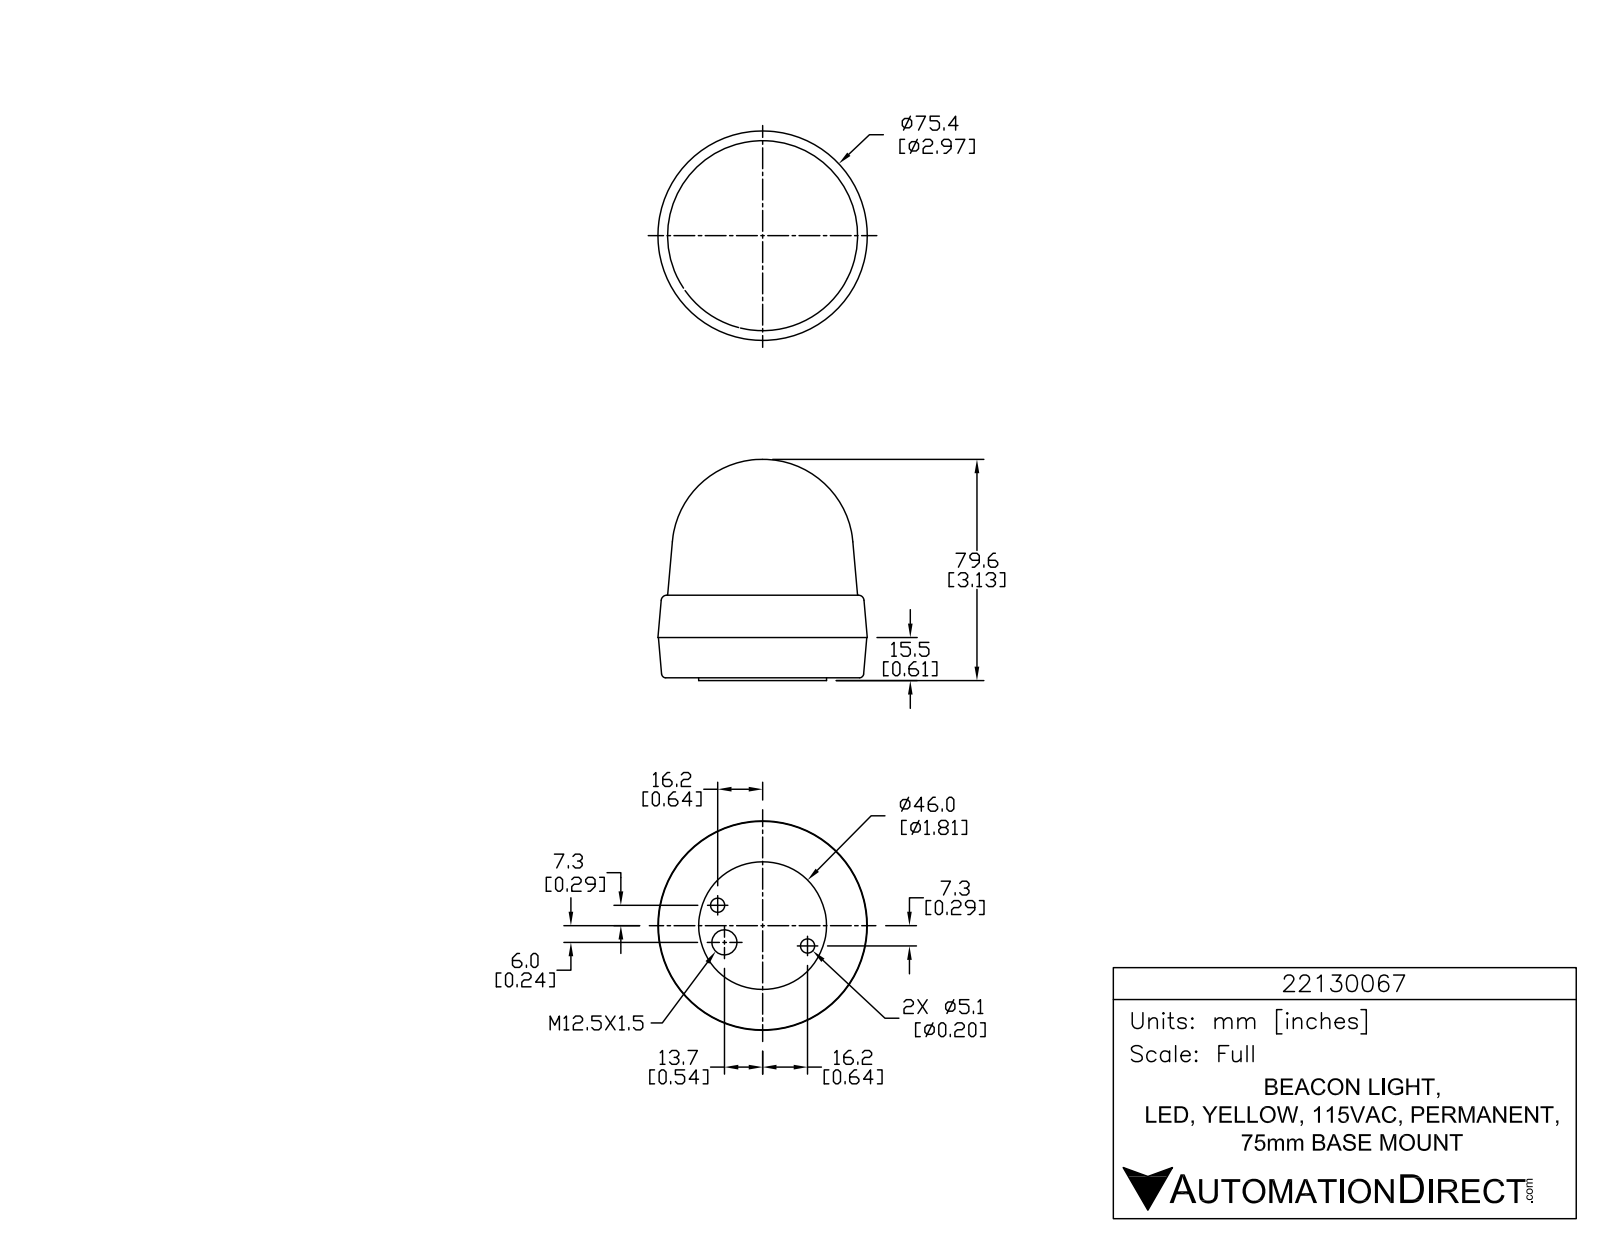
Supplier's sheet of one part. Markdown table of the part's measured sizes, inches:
| quantity | value |
| --- | --- |
| part name | 22130067 |
| STEP written by | SolidWorks 2015 (AUTOMOTIVE_DESIGN) |
| units | inches |
| bodies | 1 solid, 773 faces (526 planar, 163 cylindrical, 84 other) |
| overall size | 3.133 × 2.967 × 2.967 |
| volume | 15.79 in³ |
| surface area | 33.7 in² |
| round holes (diameter × count) | 0.059 × 3, 0.201 × 2, 0.354 × 1 |
| round bosses / shafts (diameter × count) | 0.339 × 3, 0.084 × 3, 1.811 × 1 |
| partial cylindrical surfaces (radius × count) | 0.005 × 9, 0.005 × 6, 0.012 × 6, 0.012 × 6, 0.012 × 6, 0.196 × 6, 0.005 × 3, 0.005 × 3 |
| main face-to-face distances | 0.039, 1.209, 1.17, 0.61, 0.571, 0.599, 1.566, 1.527, 0.956, 0.357 |
| hole center spacings | 0.534, 1.179, 1.398 |
